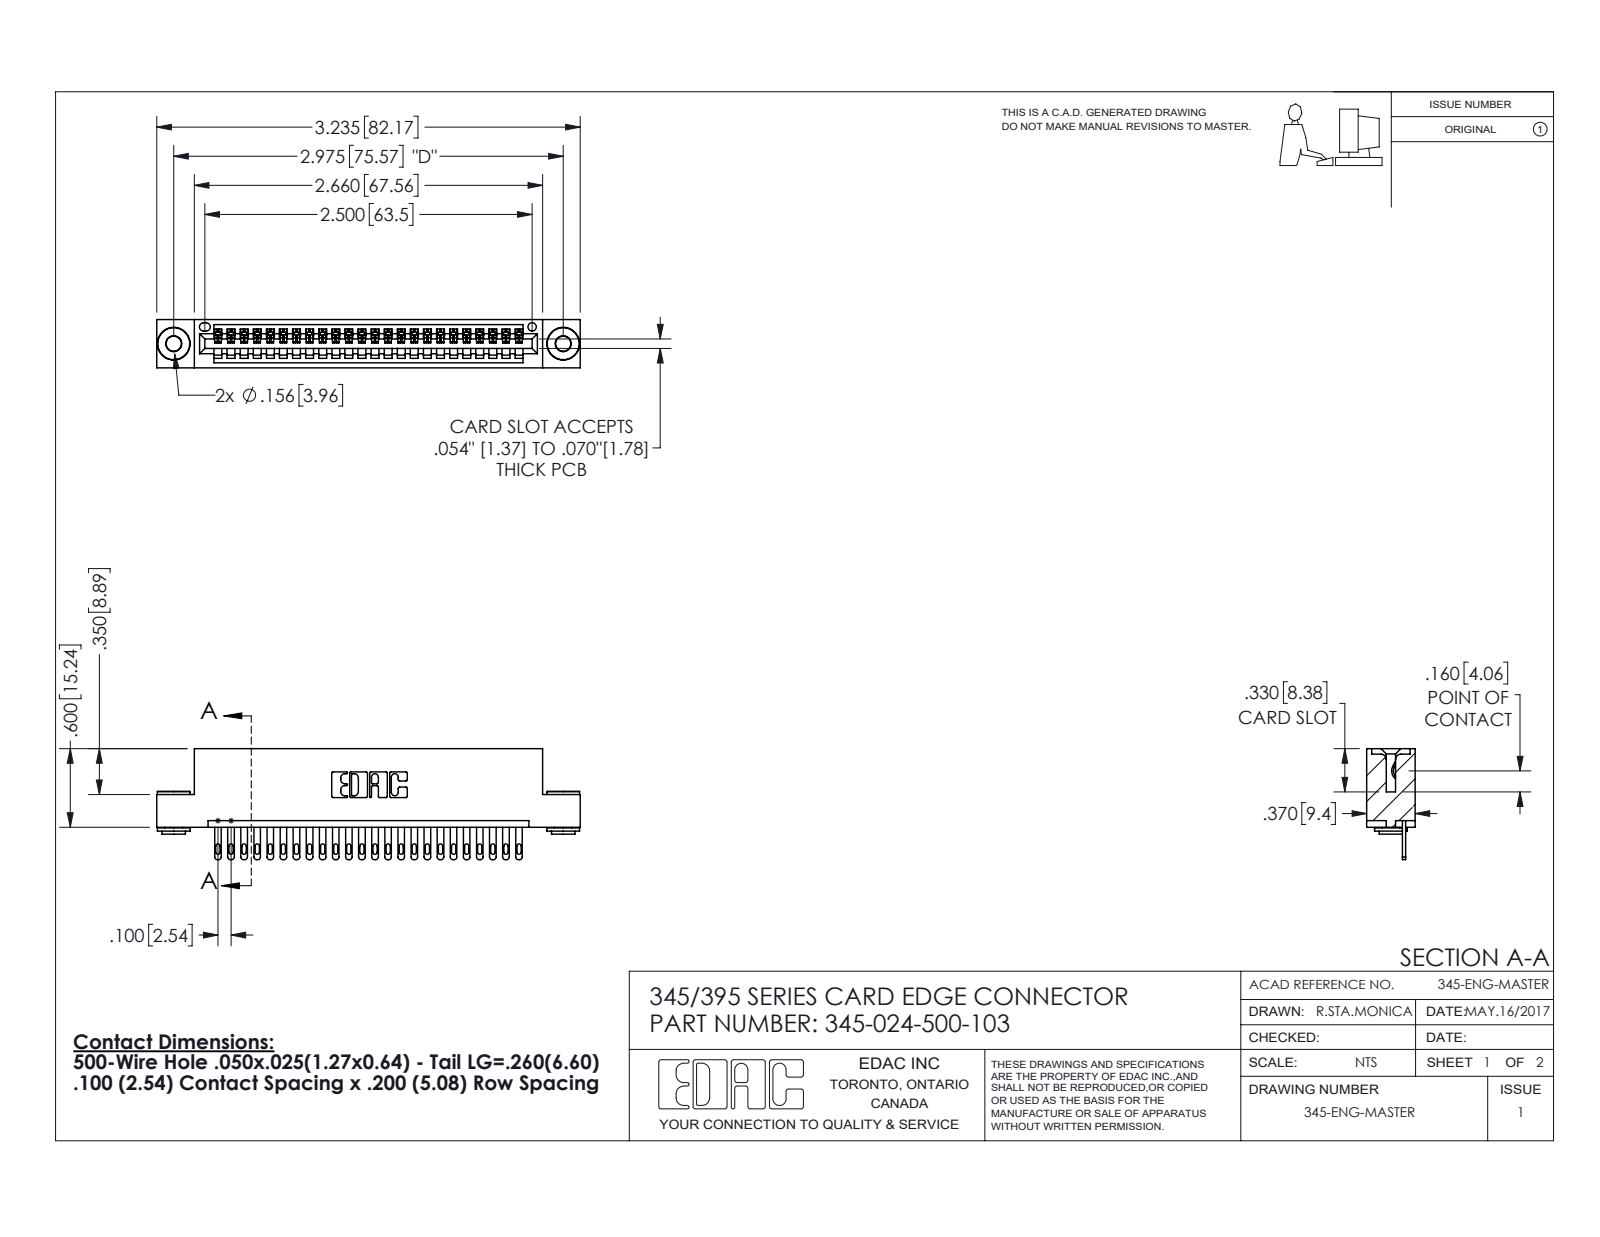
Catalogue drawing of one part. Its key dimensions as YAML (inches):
part_name: "345-024-500-103; 345 Part_Flush Mounting Lugs - 0.156 Dia-TH; 345-250-002_345-250-002-102; 345-292-001_345-293-100"
step_written_by: "SolidWorks 2016 (CONFIG_CONTROL_DESIGN)"
units: inches
bodies: {solids: 27, faces: 1460, planar: 906, cylindrical: 546, other: 8}
overall_size: [3.235, 0.847, 0.37]
volume: 0.469
surface_area: 15.88
round_holes:
  - {diameter: 0.116, count: 2}
  - {diameter: 0.156, count: 2}
  - {diameter: 0.064, count: 1}
round_bosses_or_shafts:
  - {diameter: 0.25, count: 2}
  - {diameter: 0.18, count: 2}
  - {diameter: 0.136, count: 2}
partial_cylinders:
  - {radius: 0.006, count: 48}
  - {radius: 0.016, count: 48}
  - {radius: 0.02, count: 48}
  - {radius: 0.01, count: 22}
  - {radius: 0.007, count: 6}
  - {radius: 0.031, count: 6}
  - {radius: 0.026, count: 3}
  - {radius: 0.031, count: 2}
face_to_face_distances: [0.072, 0.298, 0.2, 0.37, 0.025, 0.098, 0.272, 0.225, 0.149, 0.072]
hole_center_spacings: [0.27, 2.741, 2.975]
